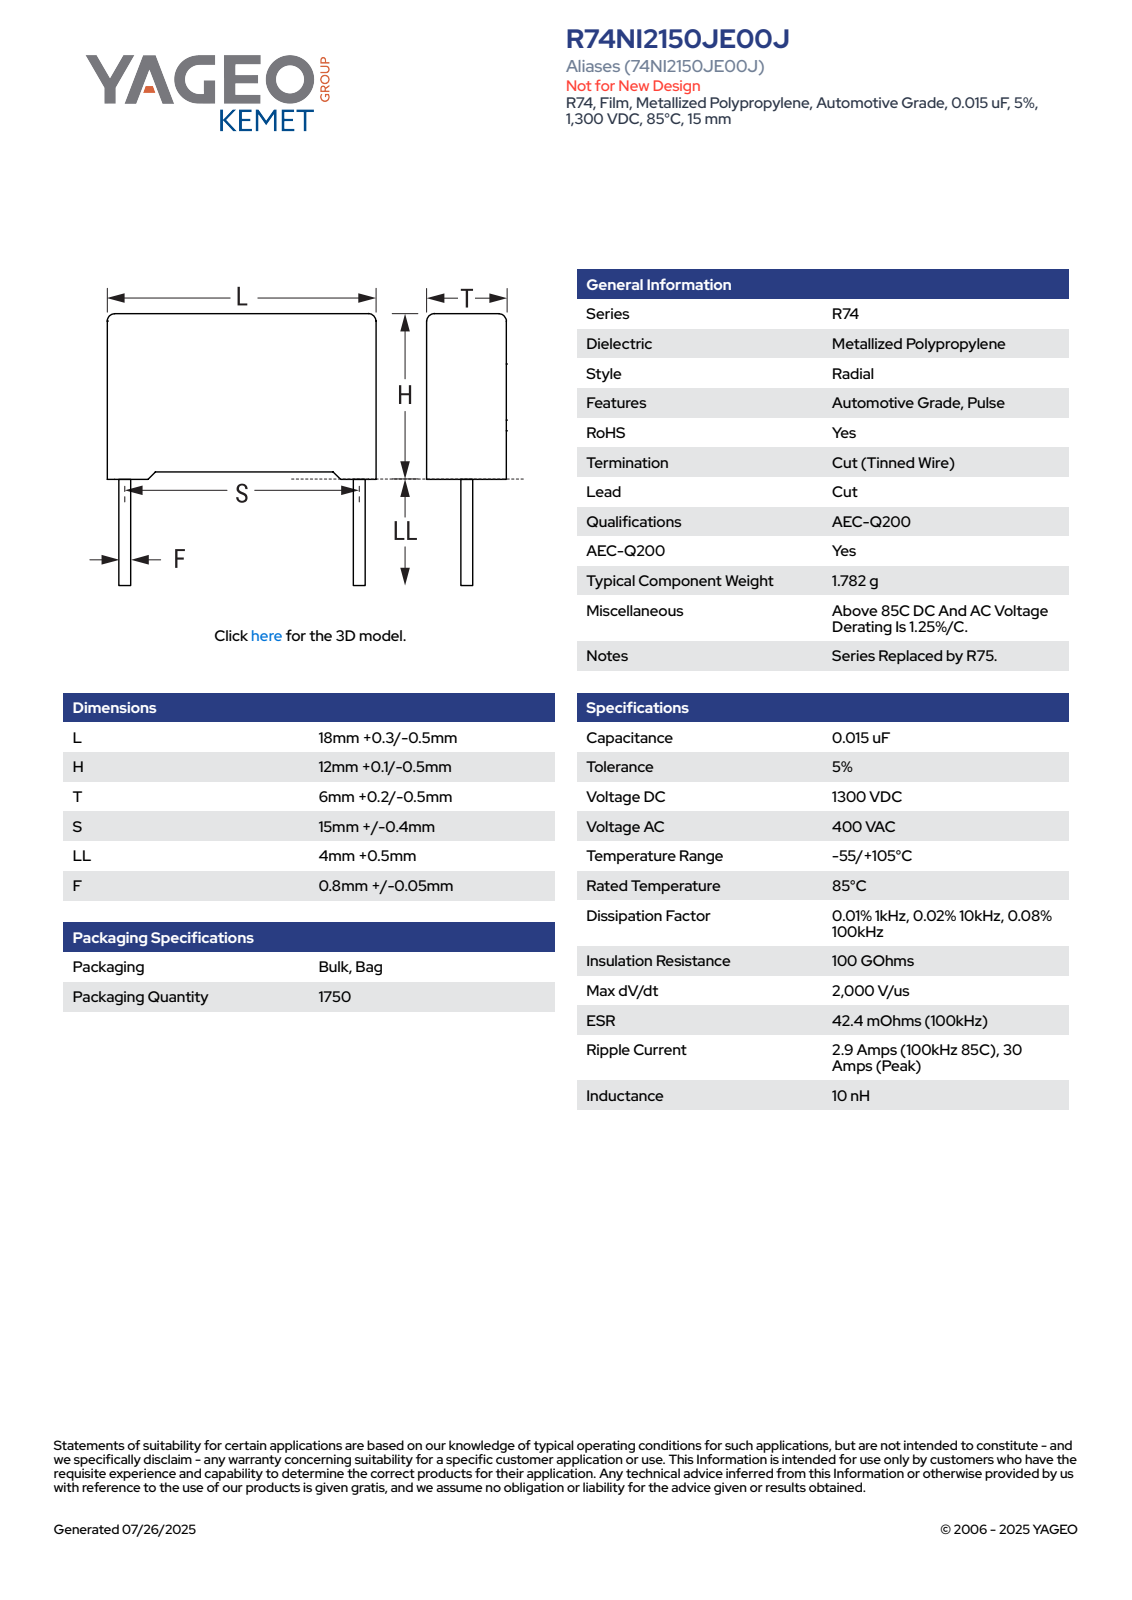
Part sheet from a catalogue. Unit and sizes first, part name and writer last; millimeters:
Units: millimetres
Overall size (bounding box): 18.3 × 16.6 × 6.21
Round bosses / shafts (diameter × count): ⌀0.85 ×2
Partial cylindrical surfaces — rounded edges, fillets, slot ends (radius × count): R0.5 ×4
Main face-to-face distances: 6.2, 11.35, 18.3, 0.61, 5.59, 0.75, 12.1, 0.42, 0.33, 11.68
Volume: 1 307 mm³ · Surface area: 877 mm²
Bodies: 4 solids, 85 faces (77 planar, 8 cylindrical, 0 other)
Part name (STEP PRODUCT): CFR_RB2_18X12X6_L18.3H12.1T6.2S15LL4.5F0.85
STEP written by: SolidWorks 2021 (AUTOMOTIVE_DESIGN)
